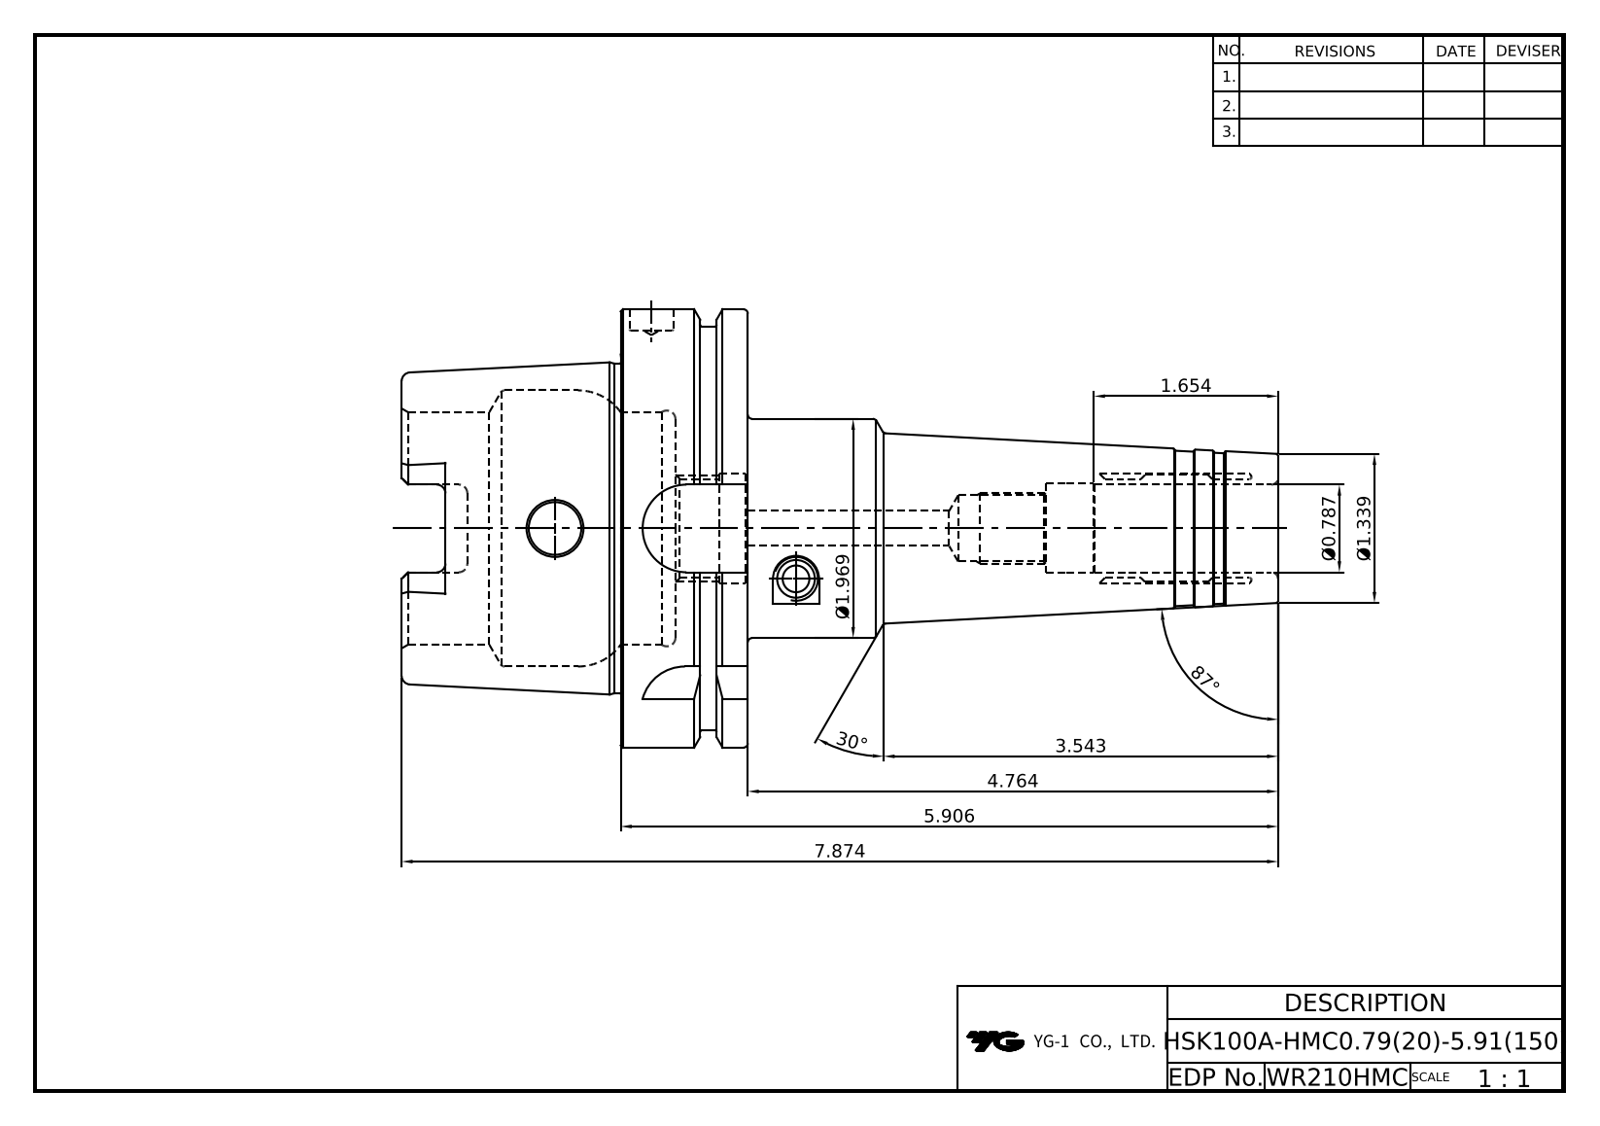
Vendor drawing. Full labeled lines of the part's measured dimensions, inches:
Part name (STEP PRODUCT): LO-HSK100A-HMC20-150
STEP written by: Autodesk Inventor 2020 (AUTOMOTIVE_DESIGN)
Units: inches
Bodies: 1 solid, 134 faces (38 planar, 35 cylindrical, 61 other)
Overall size (bounding box): 7.874 × 3.937 × 3.937
Volume: 24.3 in³ · Surface area: 108.6 in²
Round holes (diameter × count): ⌀0.315 ×1, ⌀0.394 ×1, ⌀0.472 ×1, ⌀0.587 ×1, ⌀0.787 ×1, ⌀0.803 ×1, ⌀0.881 ×1, ⌀0.984 ×1, ⌀2.087 ×1, ⌀2.48 ×1
Round bosses / shafts (diameter × count): ⌀3.937 ×1, ⌀3.622 ×1, ⌀2.969 ×1, ⌀1.969 ×1
Partial cylindrical surfaces — rounded edges, fillets, slot ends (radius × count): R0.079 ×6, R0.192 ×4, R0.394 ×4
Main face-to-face distances: 1.142, 0.492, 0.65, 2.461, 1.969, 3.11, 7.874, 5.906, 5.413, 4.764
